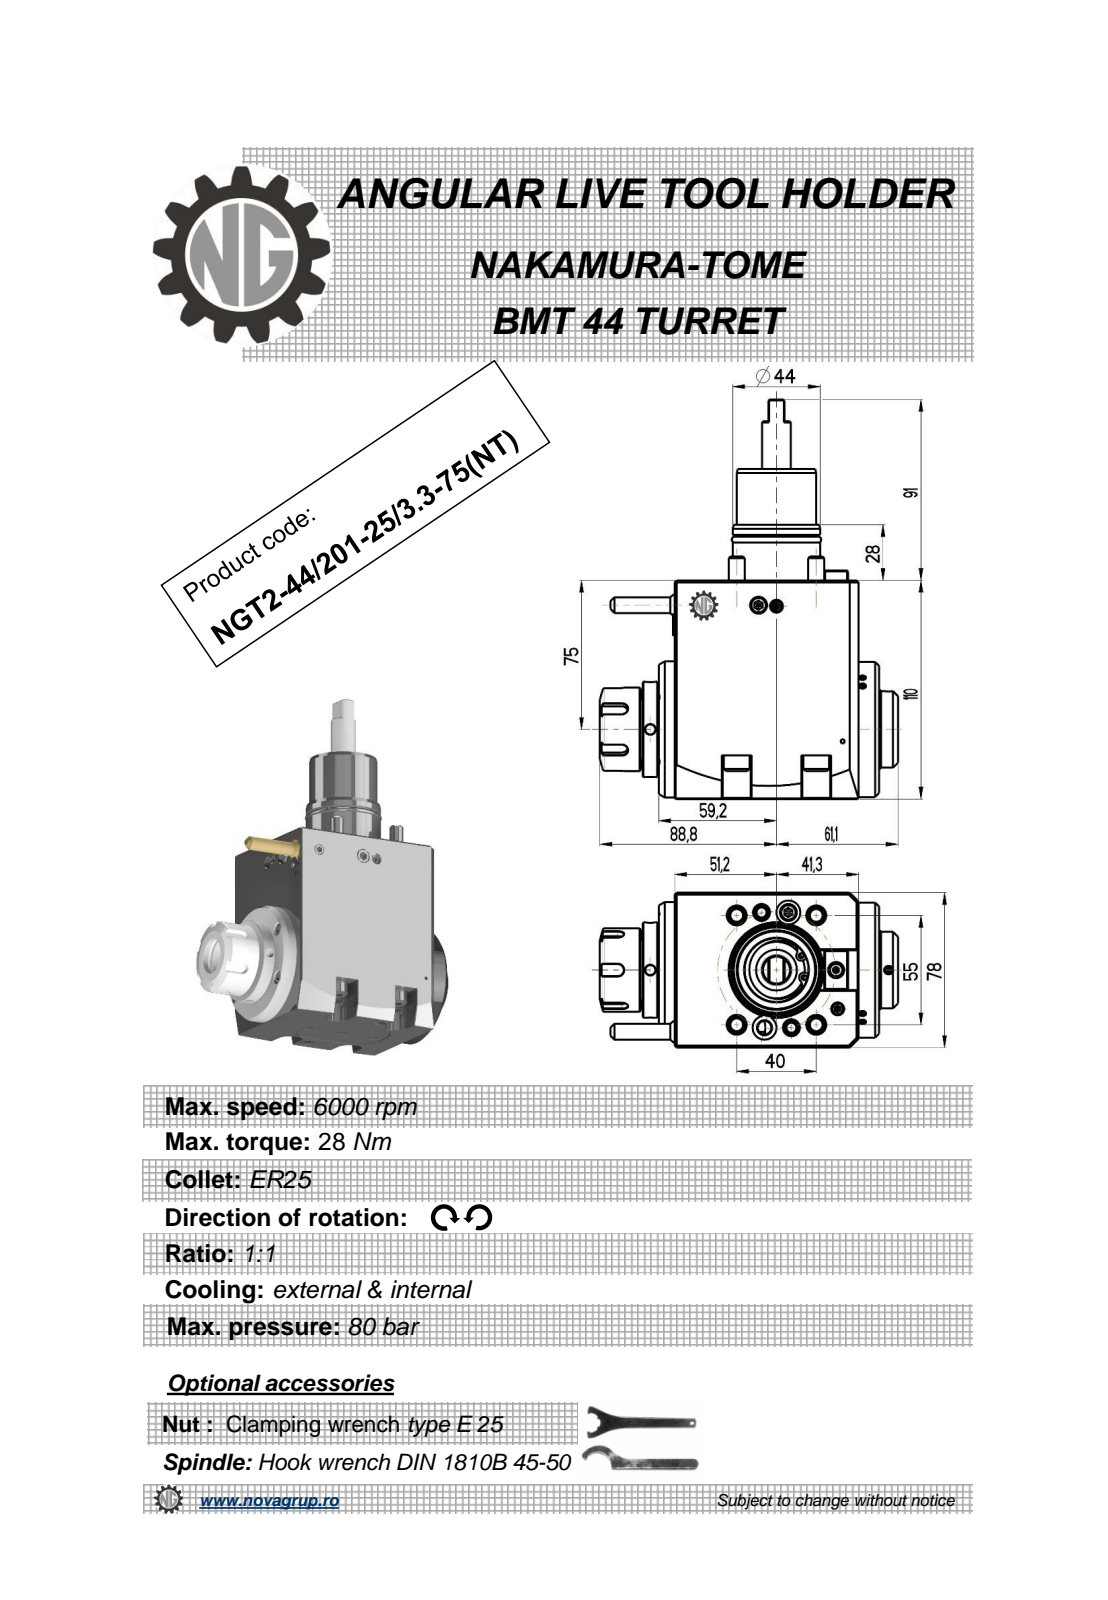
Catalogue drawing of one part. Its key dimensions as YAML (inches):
part_name: "NGT2_44_201_25_3_3_75_NT"
step_written_by: "PRO/ENGINEER BY PARAMETRIC TECHNOLOGY CORPORATION, 2010280 (CONFIG_CONTROL_DESIGN)"
units: inches
bodies: {solids: 2, faces: 399, planar: 167, cylindrical: 109, other: 123}
overall_size: [7.913, 5.902, 3.071]
volume: 59.47
surface_area: 124.8
round_holes:
  - {diameter: 0.197, count: 3}
  - {diameter: 0.268, count: 2}
  - {diameter: 0.118, count: 1}
  - {diameter: 0.799, count: 1}
round_bosses_or_shafts:
  - {diameter: 0.315, count: 5}
  - {diameter: 0.512, count: 4}
  - {diameter: 2.697, count: 1}
  - {diameter: 2.677, count: 1}
  - {diameter: 1.89, count: 1}
  - {diameter: 1.732, count: 1}
  - {diameter: 1.654, count: 1}
  - {diameter: 1.575, count: 1}
partial_cylinders:
  - {radius: 0.01, count: 20}
  - {radius: 0.009, count: 6}
  - {radius: 0.118, count: 5}
  - {radius: 0.276, count: 4}
  - {radius: 0.031, count: 2}
  - {radius: 15.354, count: 2}
face_to_face_distances: [3.071, 4.331, 3.642, 0.315, 3.957, 4.362, 4.047, 0.406, 0.551, 2.205]
hole_center_spacings: [2.332, 2.533, 2.747, 2.963]
